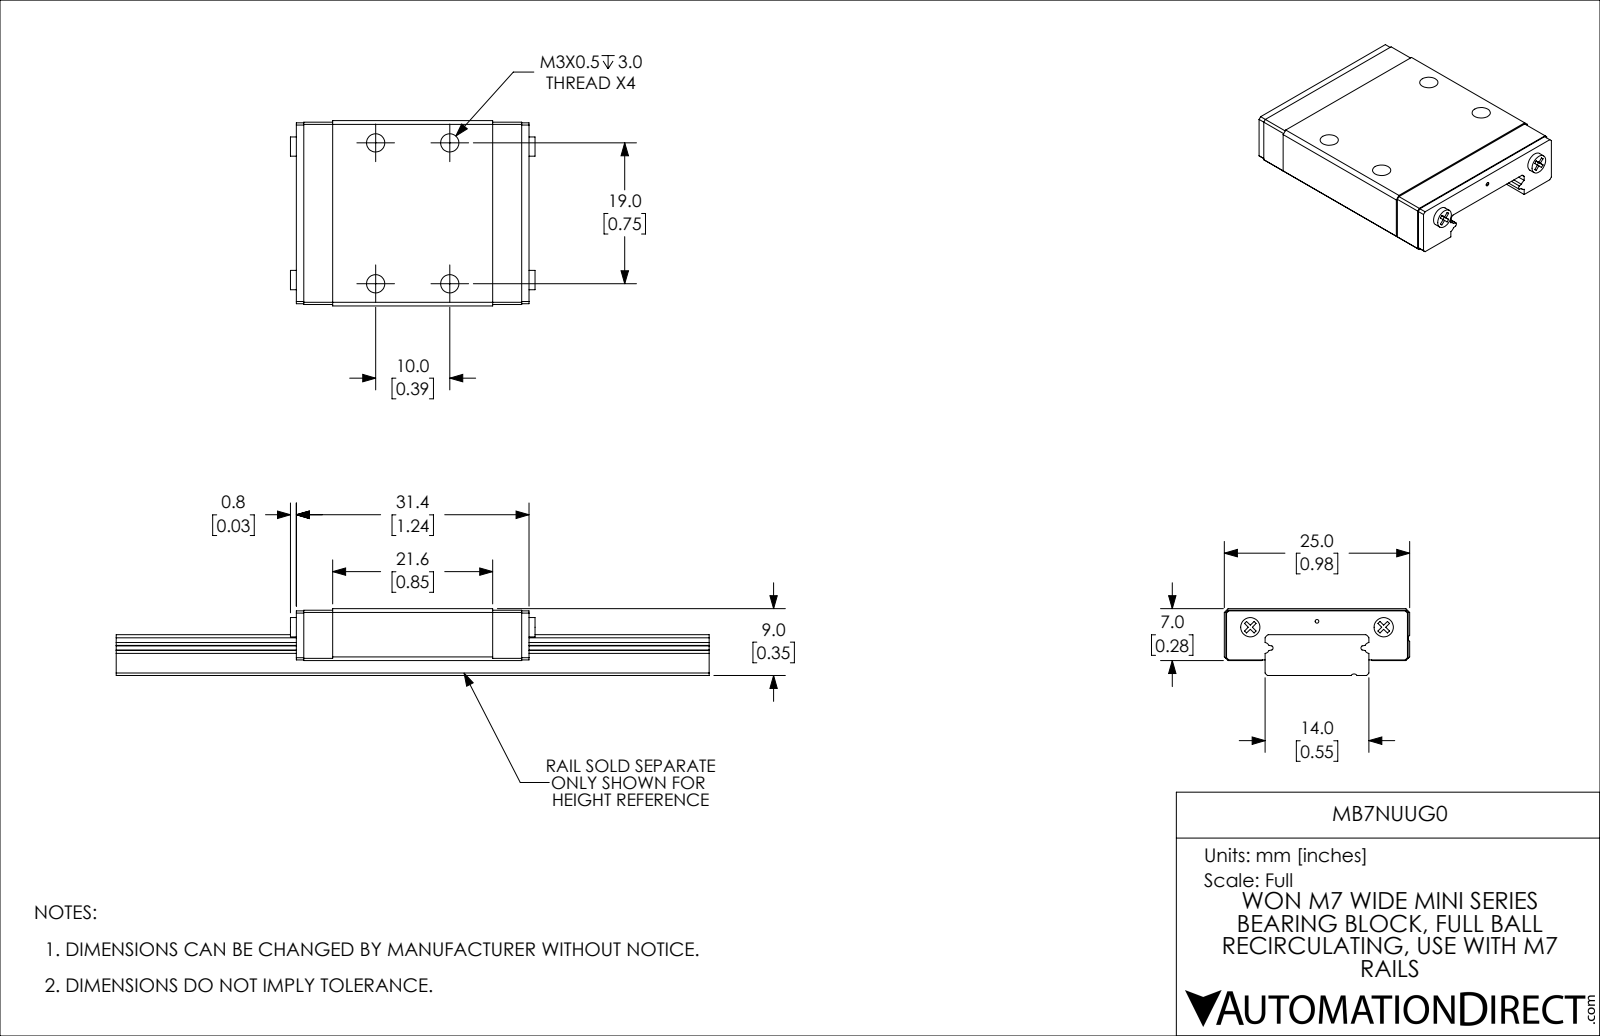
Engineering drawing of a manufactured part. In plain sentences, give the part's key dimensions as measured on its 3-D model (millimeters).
The part is named "MB7NUUG0". Its 3-D file was written by "SolidWorks 2019 (CONFIG_CONTROL_DESIGN)". It is 1 solid with 150 faces: 113 planar, 29 cylindrical and 8 other. Overall it measures 33 by 25 by 7 millimeters. Its volume is 3 868 cubic millimeters and its surface area 2 652 square millimeters. Round holes: 4 of diameter 2.46, 1 of diameter 0.5. Round bosses or shafts: 2 of diameter 2.6. Partial cylindrical surfaces (rounded edges, fillets, slot ends): 2 of radius 0.32, 2 of radius 0.75, 2 of radius 0.95, 1 of radius 0.5. The main face-to-face distances are 3.5, 7, 6.8, 3.3, 25, 31.4, 5.5, 24.8, 19.5, 5.3. The hole center spacings are 10, 19, 21.47.
